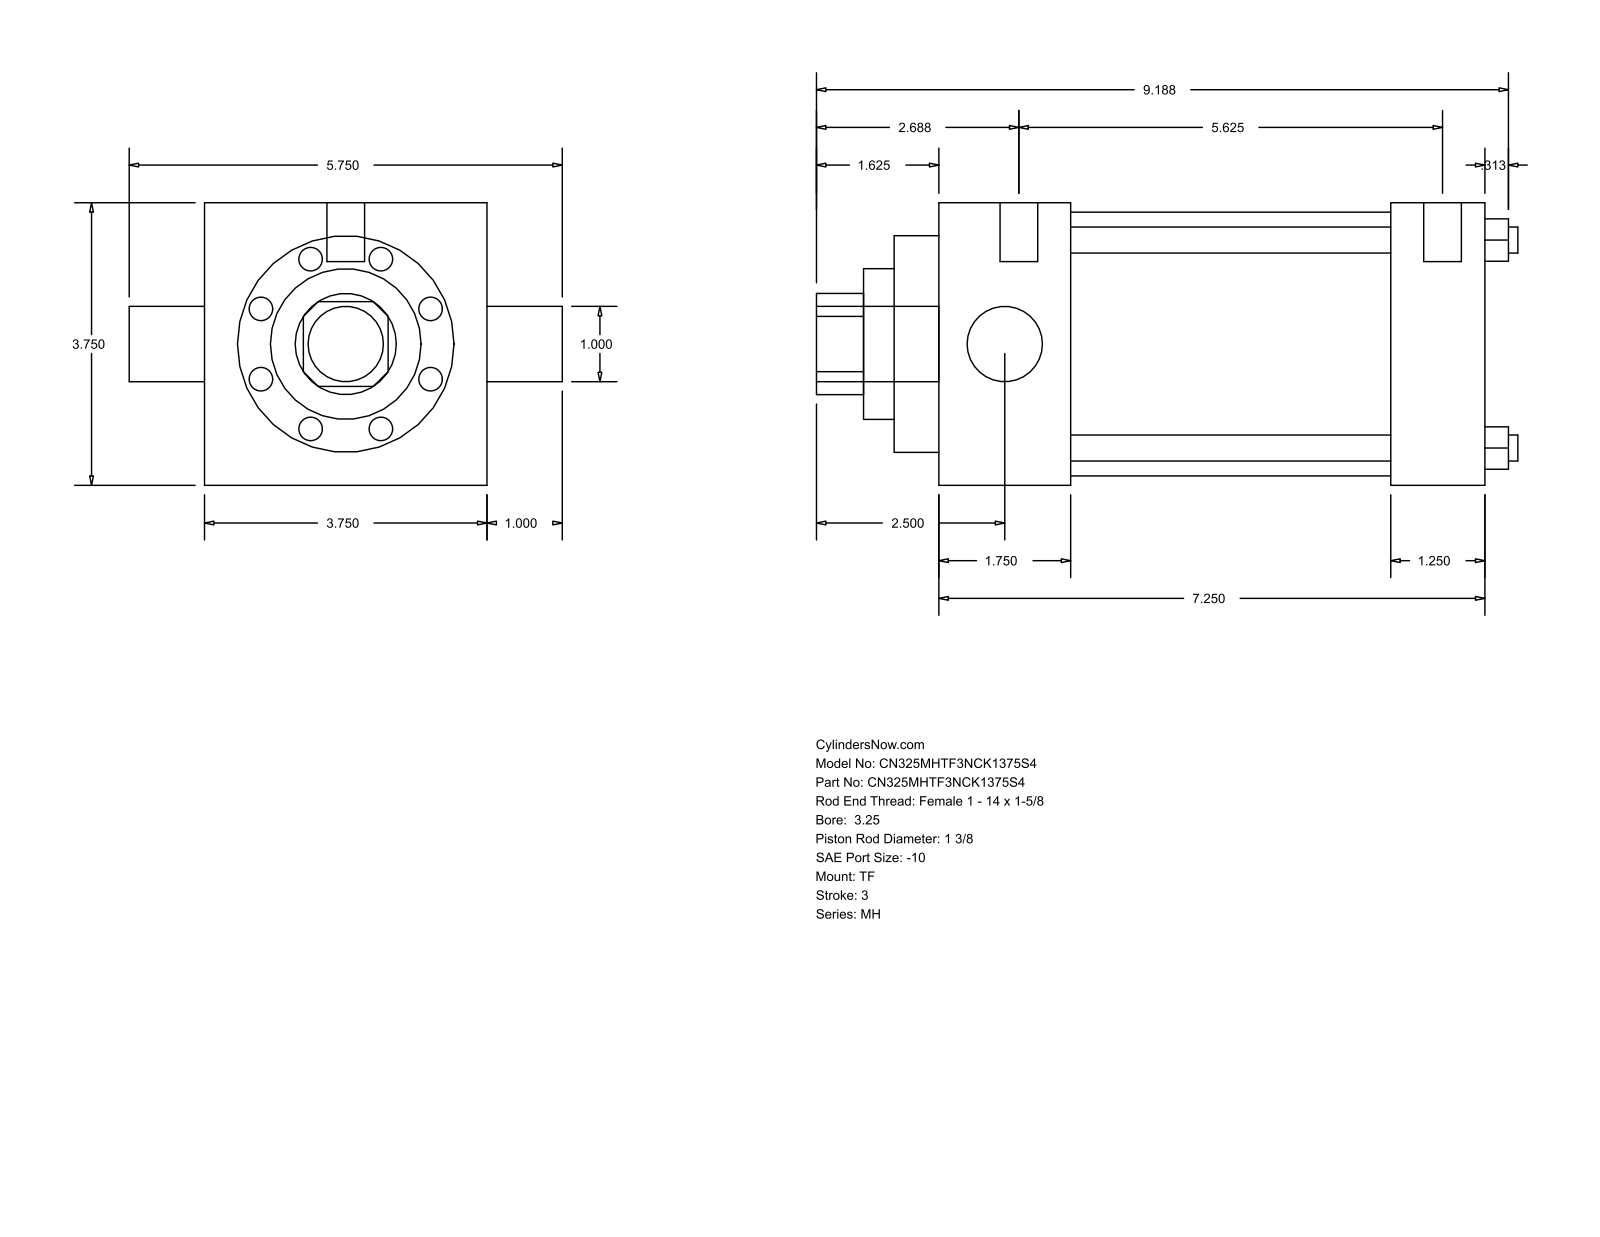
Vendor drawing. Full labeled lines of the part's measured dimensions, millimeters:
Part name (STEP PRODUCT): MH_TF__0325_1.375
STEP written by: GSSL Pune (CONFIG_CONTROL_DESIGN)
Units: millimetres
Bodies: 0 solids, 86 faces (61 planar, 25 cylindrical, 0 other)
Overall size (bounding box): 236.54 × 146.05 × 95.25
Round holes (diameter × count): ⌀8.76 ×4, ⌀25.4 ×1, ⌀34.92 ×1, ⌀50.8 ×1, ⌀73.03 ×1, ⌀88.9 ×1
Round bosses / shafts (diameter × count): ⌀5.56 ×3, ⌀12.7 ×2, ⌀25.4 ×1
Partial cylindrical surfaces — rounded edges, fillets, slot ends (radius × count): R17.06 ×1
Main face-to-face distances: 95.24, 184.16, 44.45, 152.41, 107.96, 139.71, 31.75, 15.08, 59.53, 167.49
Hole centre spacings: 49.57, 70.1, 99.14
